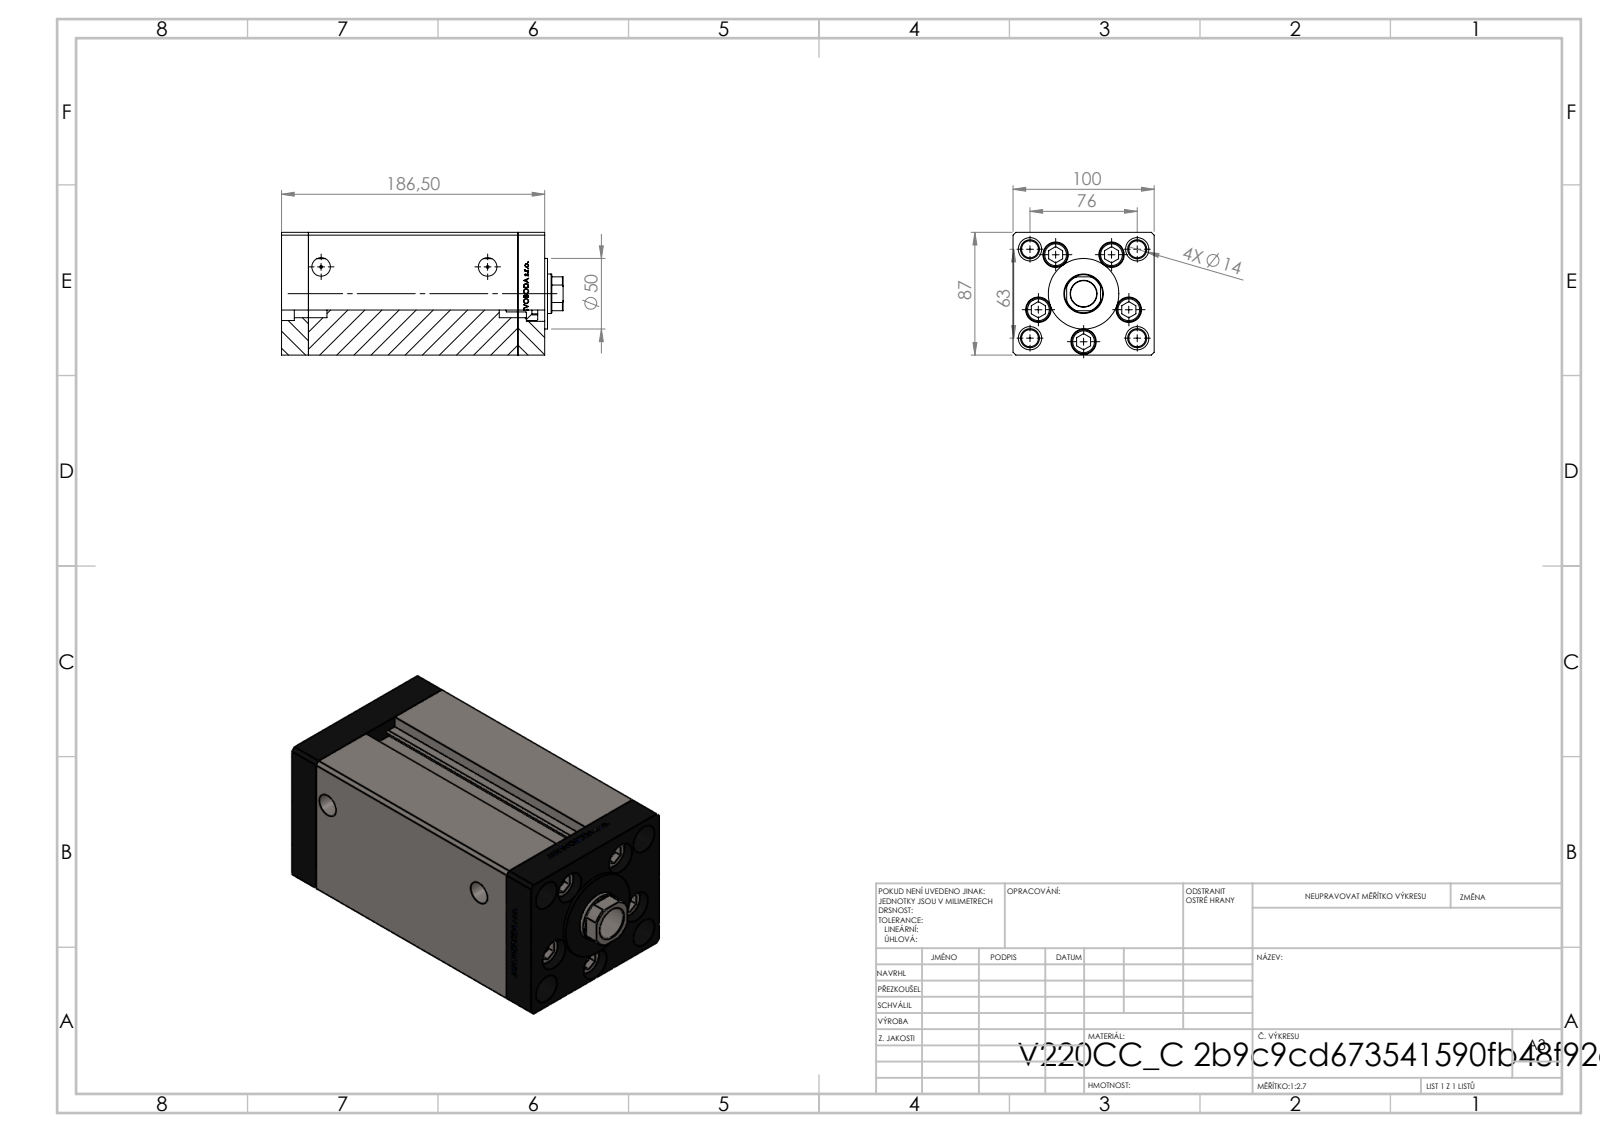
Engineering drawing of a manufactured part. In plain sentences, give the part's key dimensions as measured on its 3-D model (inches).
The part is named "V220C_VC_C; V220C BACK_C; V220C_C MIDDLE; ALLEN BOLT (+1 more)". Its 3-D file was written by "SolidWorks 2019 (CONFIG_CONTROL_DESIGN)". It is 13 solids with 1172 faces: 542 planar, 168 cylindrical and 462 other. Overall it measures 7.854 by 3.937 by 3.425 inches. Its volume is 81.28 cubic inches and its surface area 356 square inches. Round holes: 9 of diameter 0.531, 5 of diameter 0.709, 4 of diameter 0.472, 4 of diameter 0.65, 2 of diameter 0.079, 2 of diameter 0.518, 1 of diameter 0.669, 1 of diameter 0.728, 1 of diameter 1.102. Round bosses or shafts: 5 of diameter 0.315, 4 of diameter 0.669, 1 of diameter 1.969. Partial cylindrical surfaces (rounded edges, fillets, slot ends): 2 of radius 0.037, 1 of radius 0.531. The main face-to-face distances are 3.937, 3.425, 0.748, 5.846, 6.594, 1.348, 7.343, 5.994, 5.246, 0.6. The hole center spacings are 1.339, 1.943, 0.732, 0.828, 1.499, 1.546, 1.607, 1.702.
